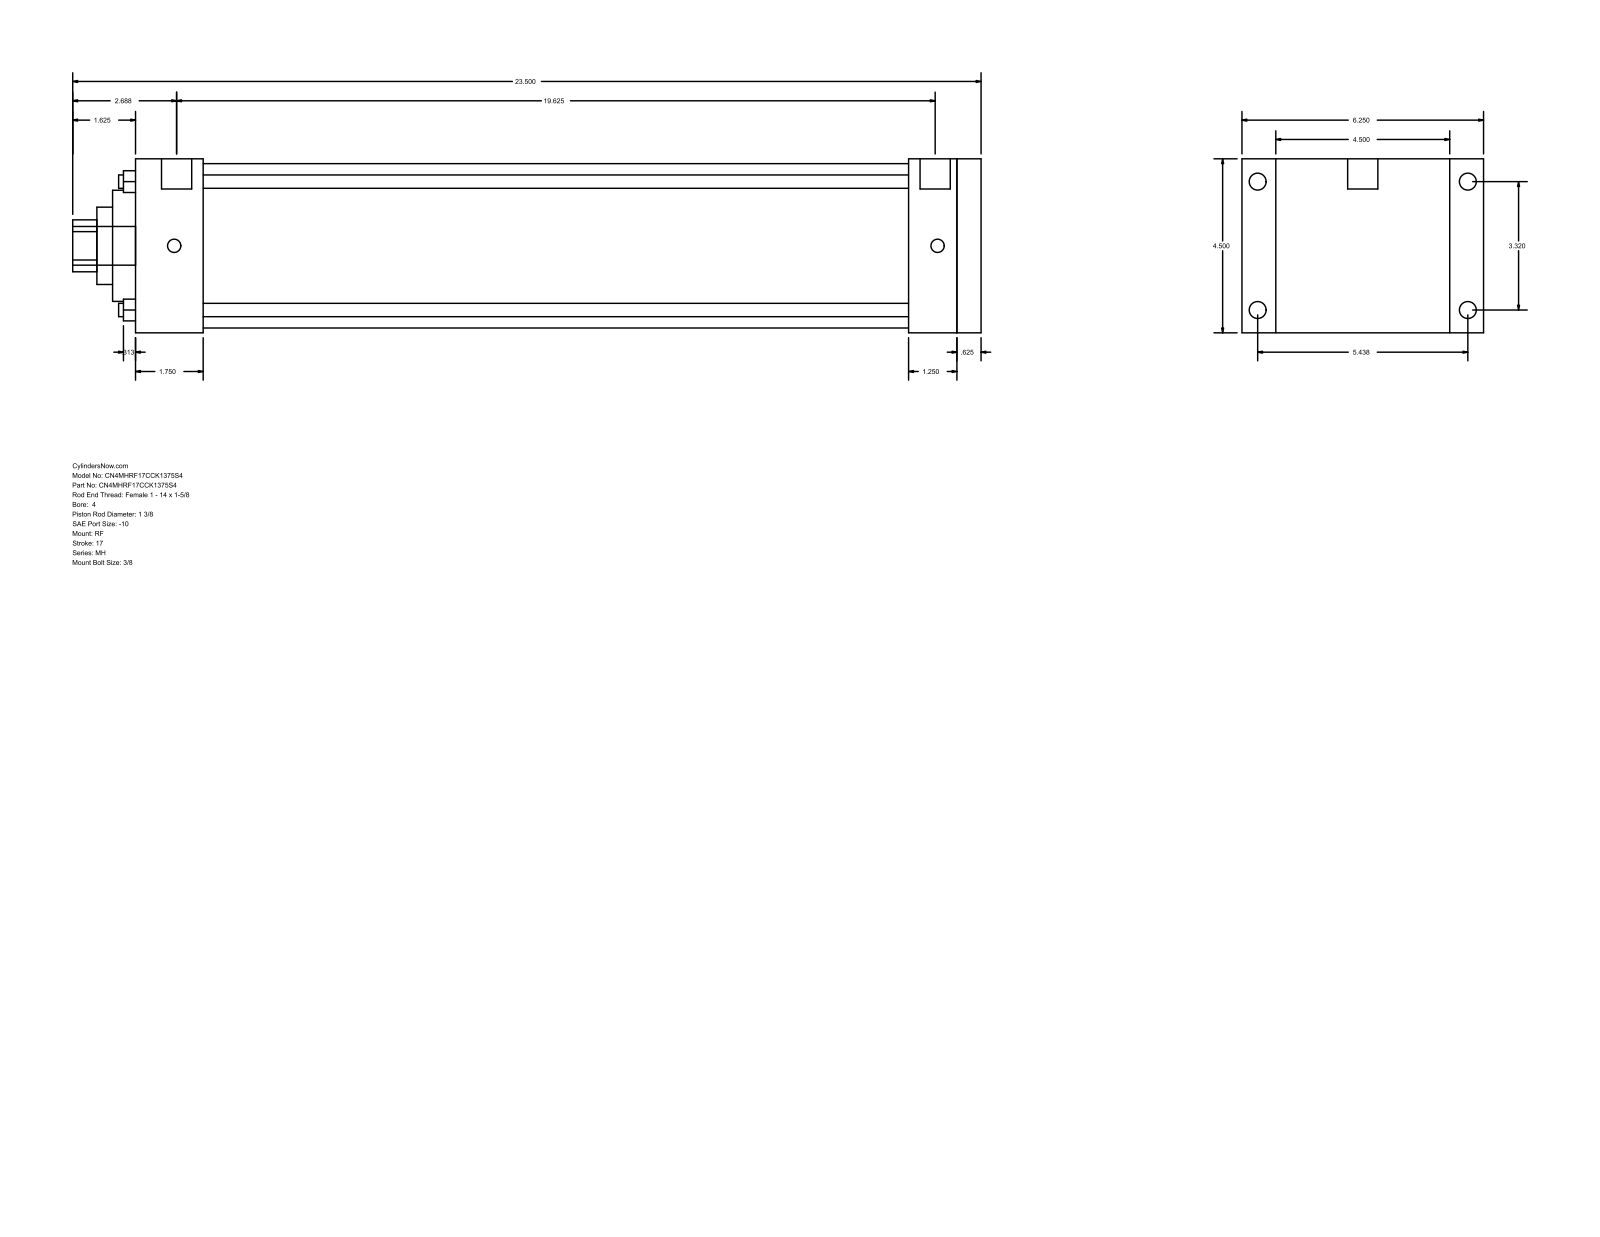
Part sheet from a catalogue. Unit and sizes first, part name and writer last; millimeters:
Units: millimetres
Overall size (bounding box): 596.9 × 158.75 × 114.3
Round holes (diameter × count): ⌀8.76 ×4, ⌀34.92 ×1, ⌀50.8 ×1, ⌀73.03 ×1, ⌀107.95 ×1
Round bosses / shafts (diameter × count): ⌀11.13 ×4, ⌀8.73 ×4, ⌀19.84 ×2, ⌀25.4 ×1
Partial cylindrical surfaces — rounded edges, fillets, slot ends (radius × count): R17.06 ×1
Main face-to-face distances: 114.3, 555.63, 15.88, 539.75, 44.45, 495.3, 511.18, 508, 463.55, 31.75
Hole centre spacings: 59.62, 84.32, 119.25
Bodies: 0 solids, 94 faces (65 planar, 29 cylindrical, 0 other)
Part name (STEP PRODUCT): MH_RF__0400_1.375
STEP written by: GSSL Pune (CONFIG_CONTROL_DESIGN)
